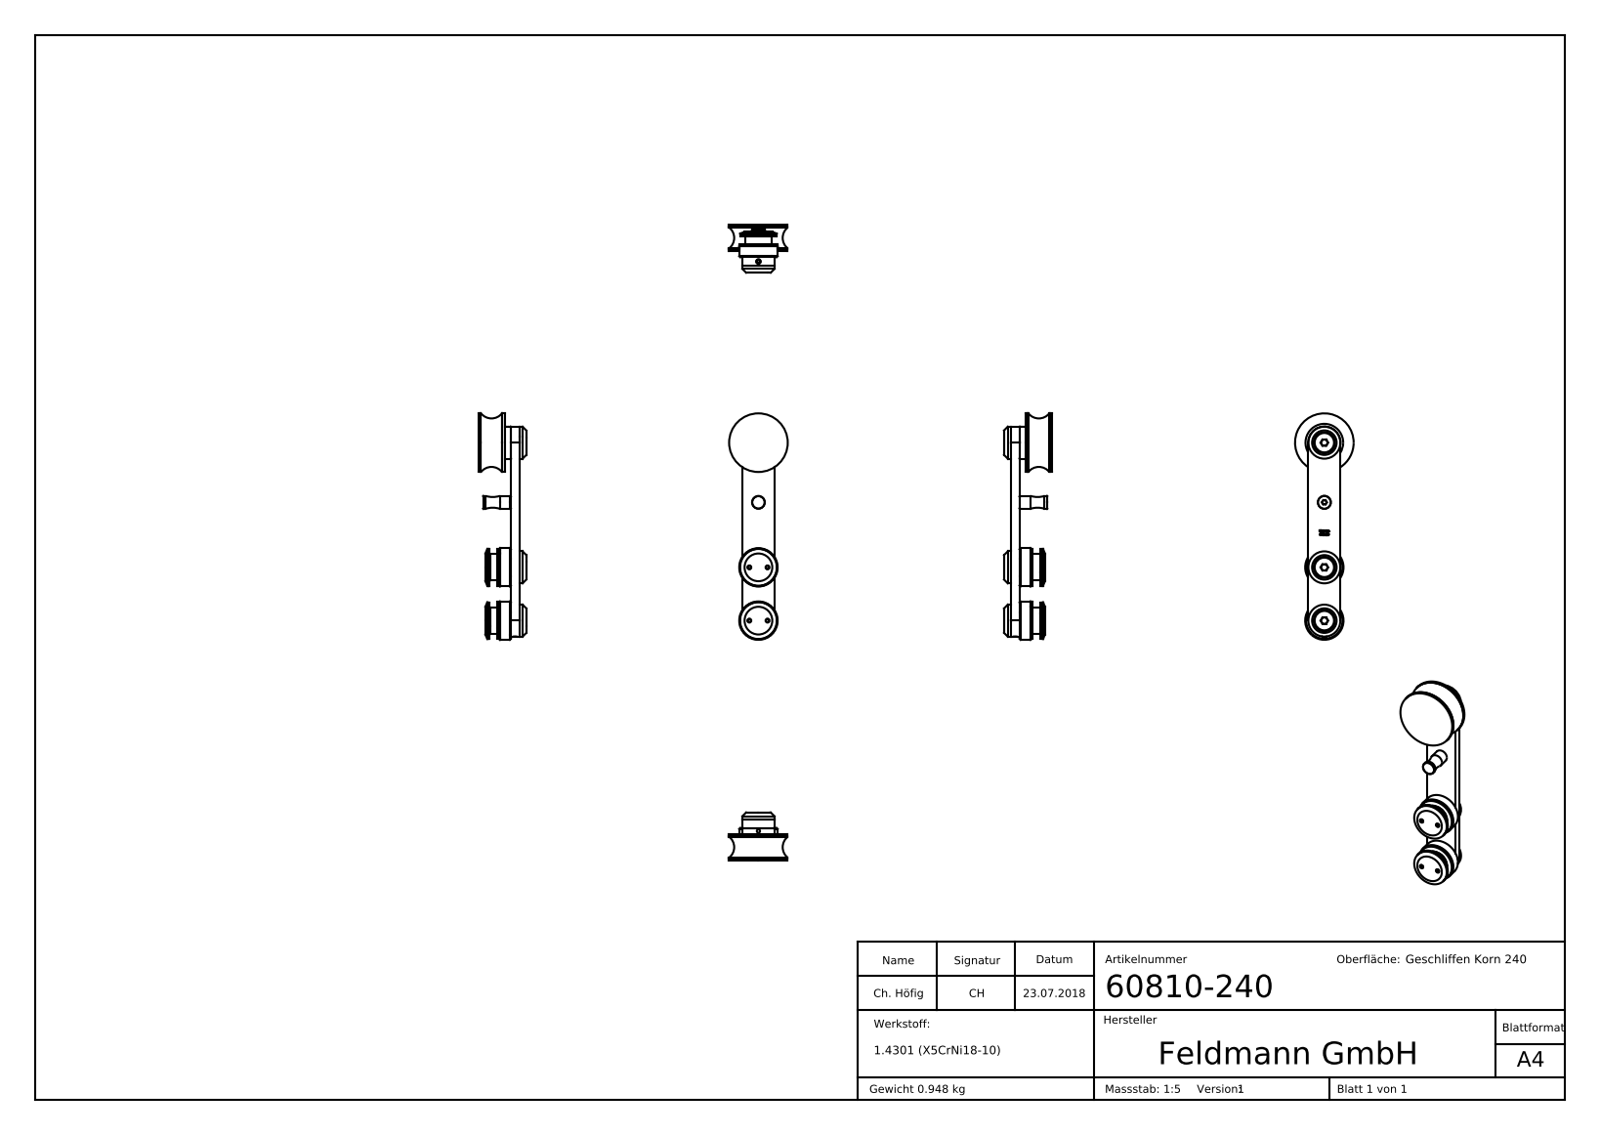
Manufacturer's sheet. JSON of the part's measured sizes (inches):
{"part_name": "radial ball bearing_68_din_DIN 625 - 6002 - 12,DE,AC,12_68; 6081X-240 Teil6_6081X-240 Teil6; 6081X-240 Teil4_6081X-240 Teil4; 6081X-240 Teil3_6081X-240 Teil3 (+8 more)", "step_written_by": "SolidWorks 2015 (CONFIG_CONTROL_DESIGN)", "units": "inches", "bodies": {"solids": 26, "faces": 987, "planar": 275, "cylindrical": 285, "other": 427}, "overall_size": [8.366, 2.165, 1.772], "volume_in3": 8.7, "surface_area_in2": 129.6, "round_holes": [[0.118, 9], [0.335, 3], [0.512, 3], [0.717, 3], [1.339, 3], [0.067, 2], [0.669, 2], [0.748, 2], [1, 2], [0.165, 1], [0.197, 1], [0.256, 1]], "round_bosses_or_shafts": [[1.378, 3], [1.181, 3], [0.787, 3], [0.394, 3], [1.417, 2], [1.358, 2], [1.299, 2], [0.965, 2]], "partial_cylinders_radius": [[0.201, 4], [0.008, 2], [0.02, 2], [0.331, 1], [0.413, 1]], "face_to_face_distances": [0.315, 0.079, 0.807, 0.886, 0.256, 0.512, 0.118, 0.295, 0.394, 0.039], "hole_center_spacings": [0.335, 0.365, 0.492, 0.758, 1.997, 1.969, 0.343, 0.669]}
